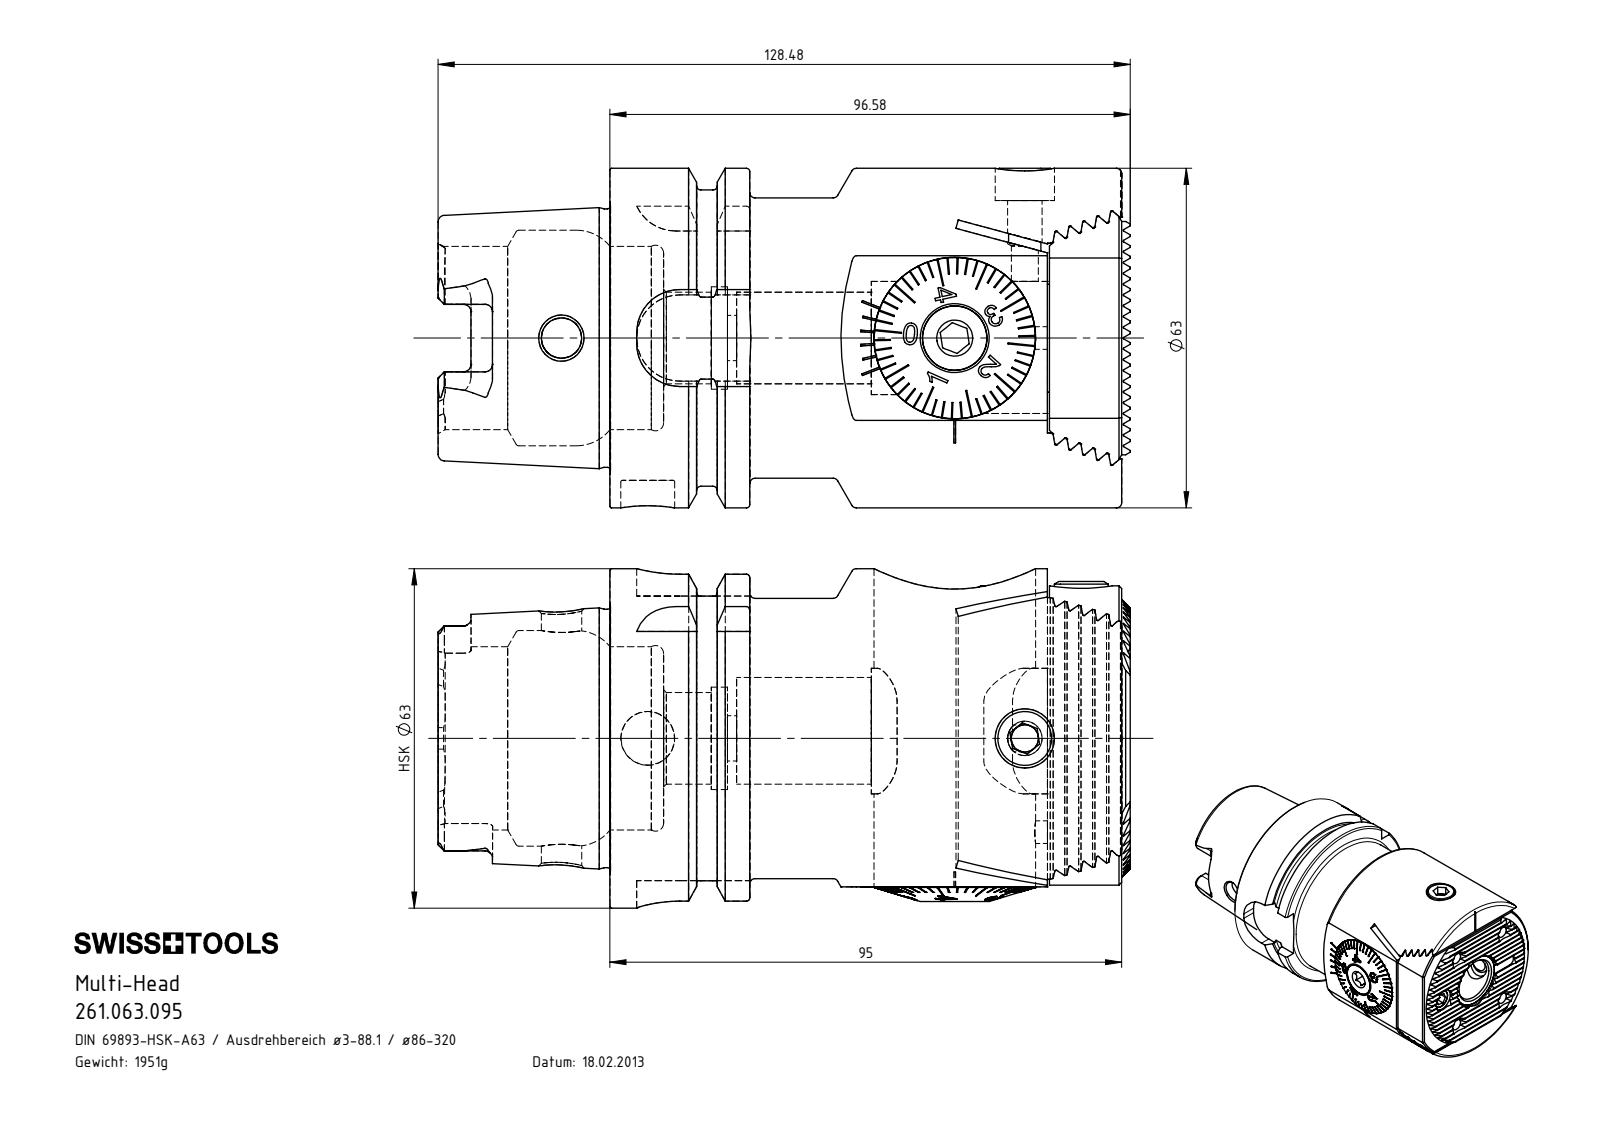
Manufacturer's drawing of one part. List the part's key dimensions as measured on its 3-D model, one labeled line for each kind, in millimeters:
Part name (STEP PRODUCT): MH1-BG3.001.042_D; HA6-MH1.K00.095_A_Fertigbearbeitung; MH1-BG2.001.056_D; MH1-BG1.004.049 (+8 more)
STEP written by: SolidWorks 2017 (CONFIG_CONTROL_DESIGN)
Units: millimetres
Bodies: 15 solids, 1176 faces (570 planar, 265 cylindrical, 341 other)
Overall size (bounding box): 128.48 × 63 × 63
Volume: 248 599 mm³ · Surface area: 75 928 mm²
Round holes (diameter × count): ⌀4.2 ×5, ⌀8.5 ×4, ⌀6.8 ×3, ⌀11 ×3, ⌀20 ×2, ⌀1 ×1, ⌀1.6 ×1, ⌀3.3 ×1, ⌀5 ×1, ⌀6.4 ×1, ⌀7.5 ×1, ⌀8 ×1
Round bosses / shafts (diameter × count): ⌀10 ×3, ⌀63 ×1, ⌀54.95 ×1, ⌀52 ×1, ⌀47.94 ×1, ⌀30 ×1, ⌀29.98 ×1, ⌀29.9 ×1
Partial cylindrical surfaces — rounded edges, fillets, slot ends (radius × count): R0.14 ×21, R0.2 ×20, R1.4 ×6, R6 ×6, R2.88 ×4, R8 ×4, R4 ×2, R31 ×2
Main face-to-face distances: 2.38, 0.4, 4.76, 1.73, 81.2, 81.6, 8.66, 5.2, 13.4, 95
Hole centre spacings: 16.73, 18.03, 20.52, 24, 30, 34.8, 38.42, 7.28
